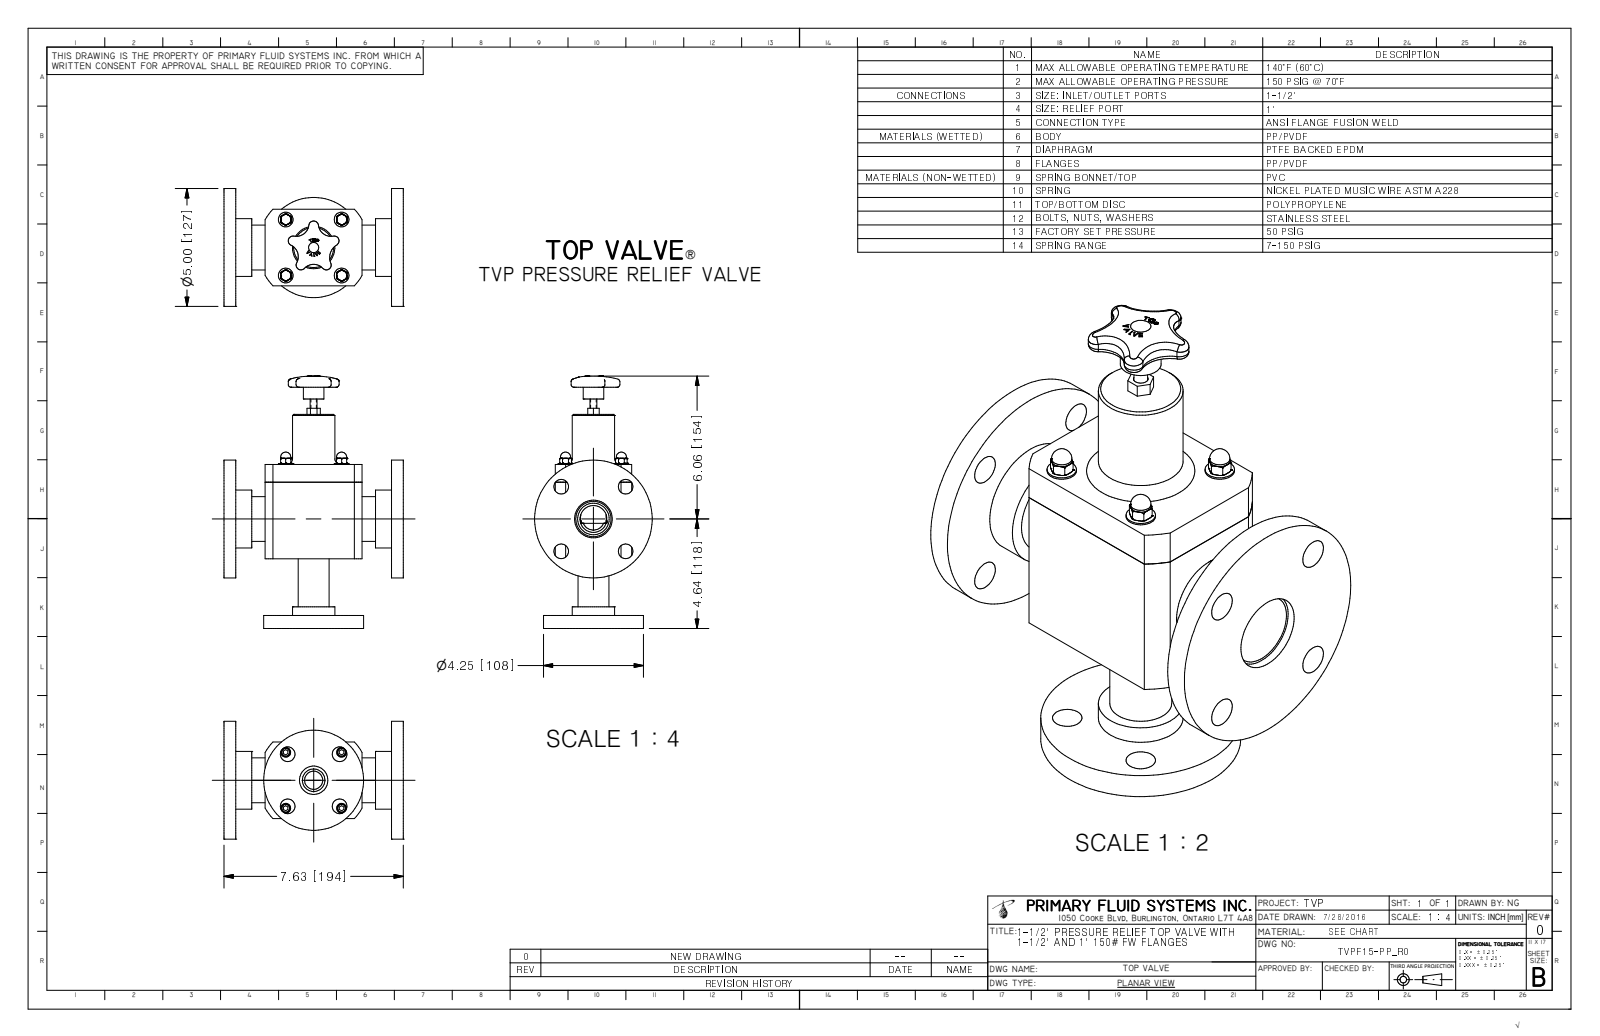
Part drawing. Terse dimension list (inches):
name: TVPF15-PP_R0
written by: Autodesk Inventor 2009 (AUTOMOTIVE_DESIGN)
unit: in
bodies: 1 solid, 376 faces (157 planar, 70 cylindrical, 149 other)
size: 10.704 × 7.625 × 5
volume: 85.87 in³; area: 295.4 in²
holes: 4× ⌀0.175, 4× ⌀0.62, 4× ⌀0.625, 1× ⌀0.957, 1× ⌀1.205, 1× ⌀1.5, 1× ⌀1.6
bosses: 4× ⌀0.625, 4× ⌀0.433, 4× ⌀0.375, 1× ⌀5, 1× ⌀4.25, 1× ⌀2.45, 1× ⌀1.9, 1× ⌀1.8
rounds: 5× R0.085, 5× R0.205, 4× R0.536, 4× R0.656, 1× R0.625, 1× R0.745, 1× R2.375
face distances: 0.5, 7.125, 7.625, 3.25, 6.625, 1.75, 5.875, 1.25, 5.375, 2.954
hole spacings: 1.562, 1.937, 2.209, 2.294, 2.74, 0.117, 0.117, 1.679
